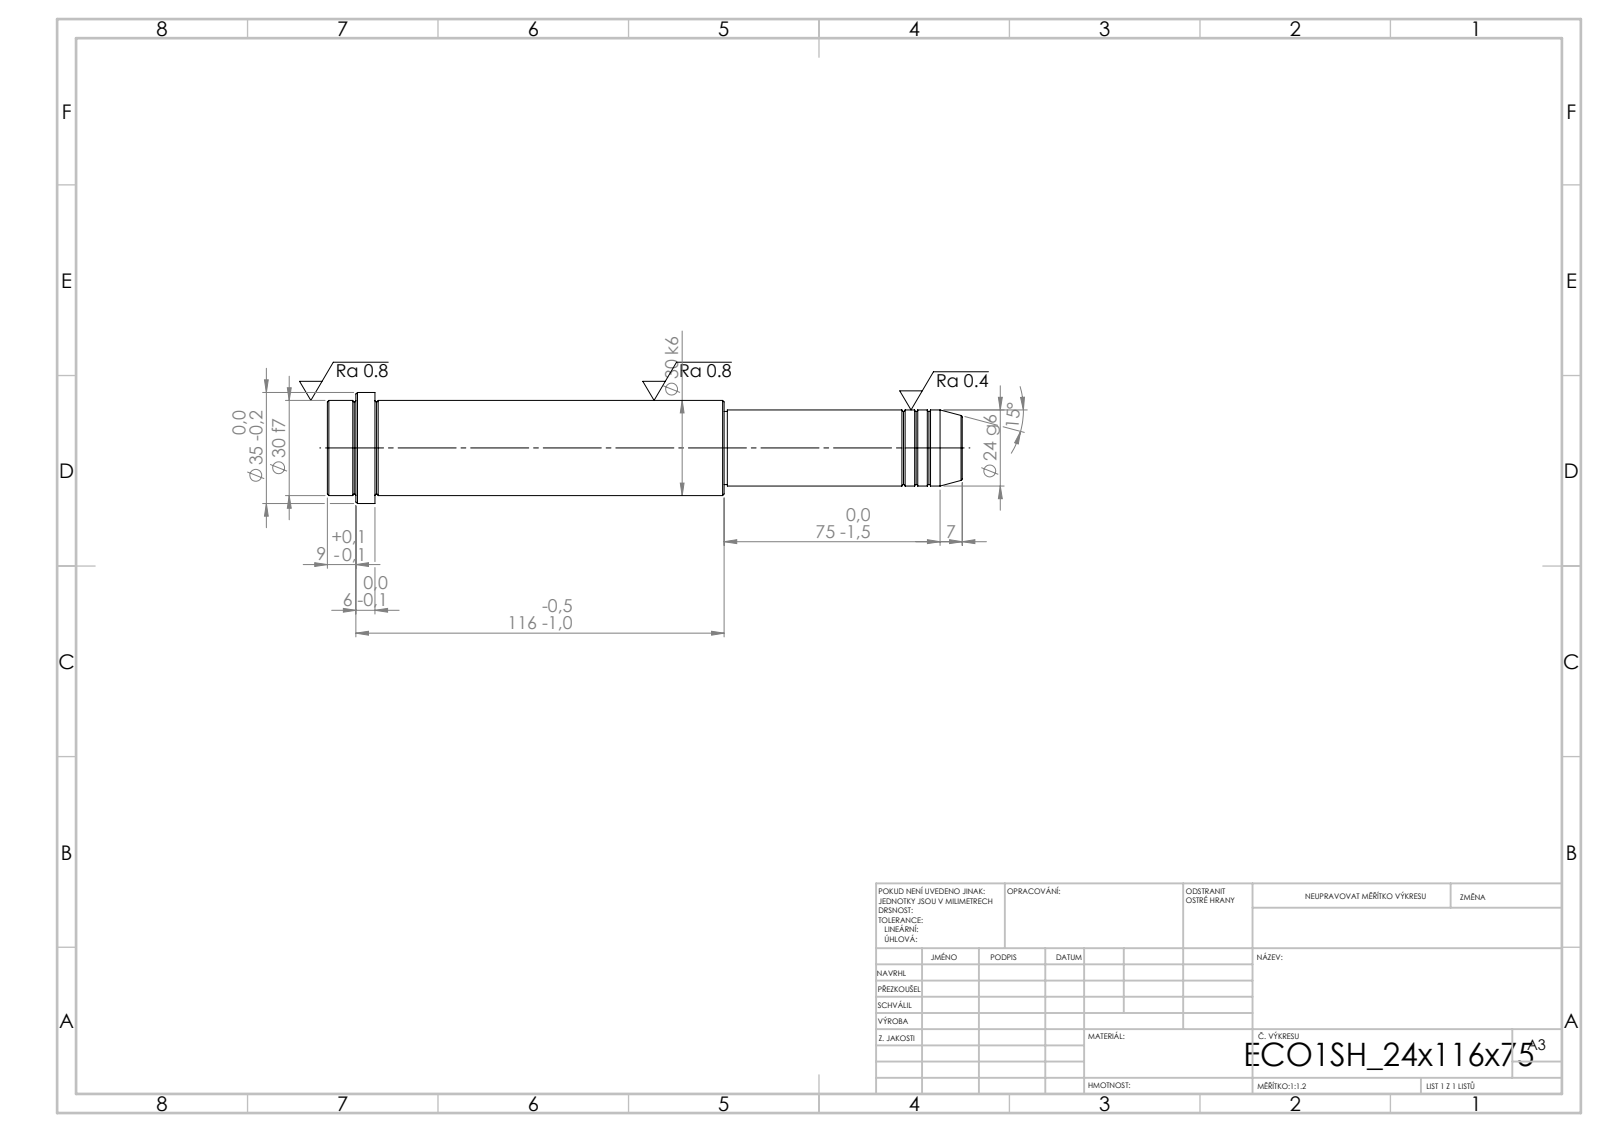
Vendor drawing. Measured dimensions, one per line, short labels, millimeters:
written by: SolidWorks 2019 (CONFIG_CONTROL_DESIGN)
unit: mm
bodies: 1 solid, 52 faces (6 planar, 16 cylindrical, 30 other)
size: 200 × 35 × 35
volume: 123 113 mm³; area: 19 496 mm²
bosses: 1× ⌀35, 1× ⌀30, 1× ⌀24, 1× ⌀23
face distances: 200, 185, 15, 75, 110, 125, 191, 116, 6, 9
